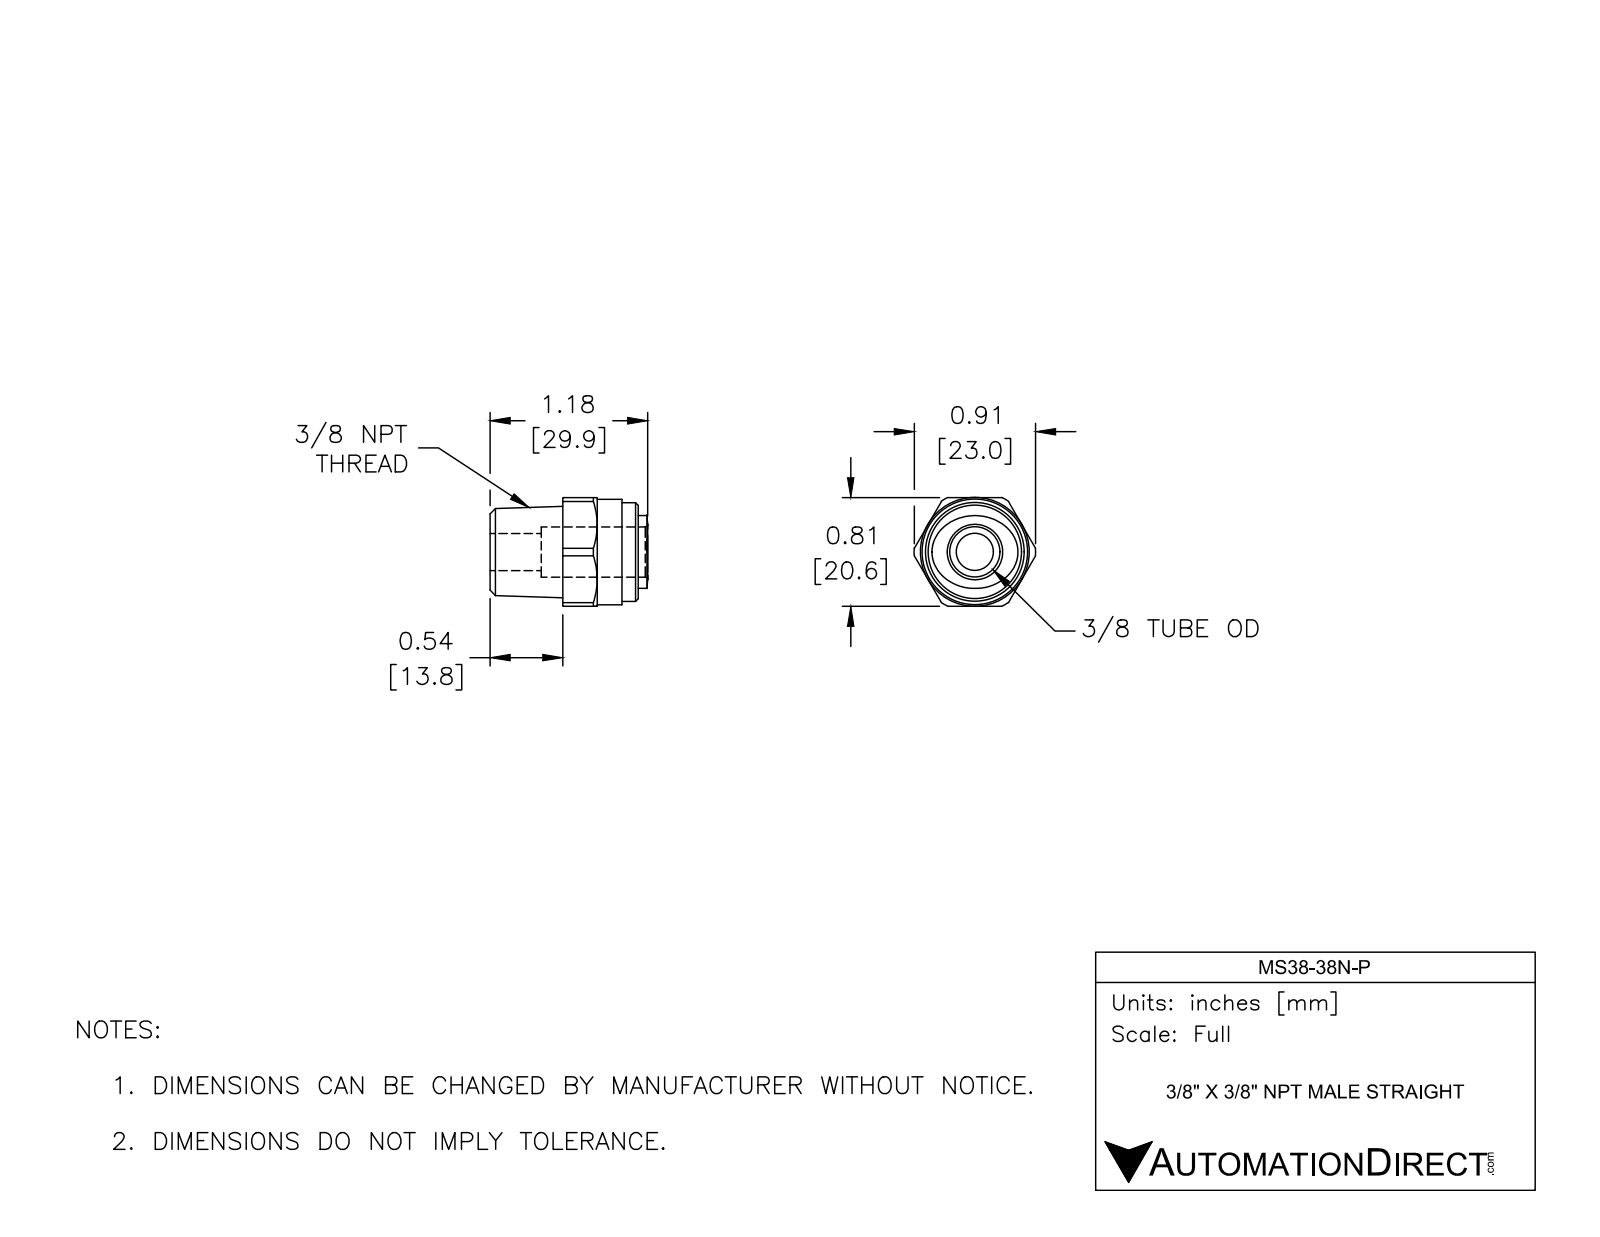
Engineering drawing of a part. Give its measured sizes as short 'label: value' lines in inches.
name: MS38-38N-P
written by: SolidWorks 2017 (AUTOMOTIVE_DESIGN)
unit: in
bodies: 1 solid, 46 faces (12 planar, 15 cylindrical, 19 other)
size: 1.177 × 0.906 × 0.811
volume: 0.382 in³; area: 4.837 in²
holes: 1× ⌀0.276, 1× ⌀0.374
bosses: 1× ⌀0.787, 1× ⌀0.736
rounds: 1× R0.453
face distances: 0.811, 0.543, 1.106, 0.563, 0.984, 0.441, 0.122, 0.382, 0.161, 0.602
